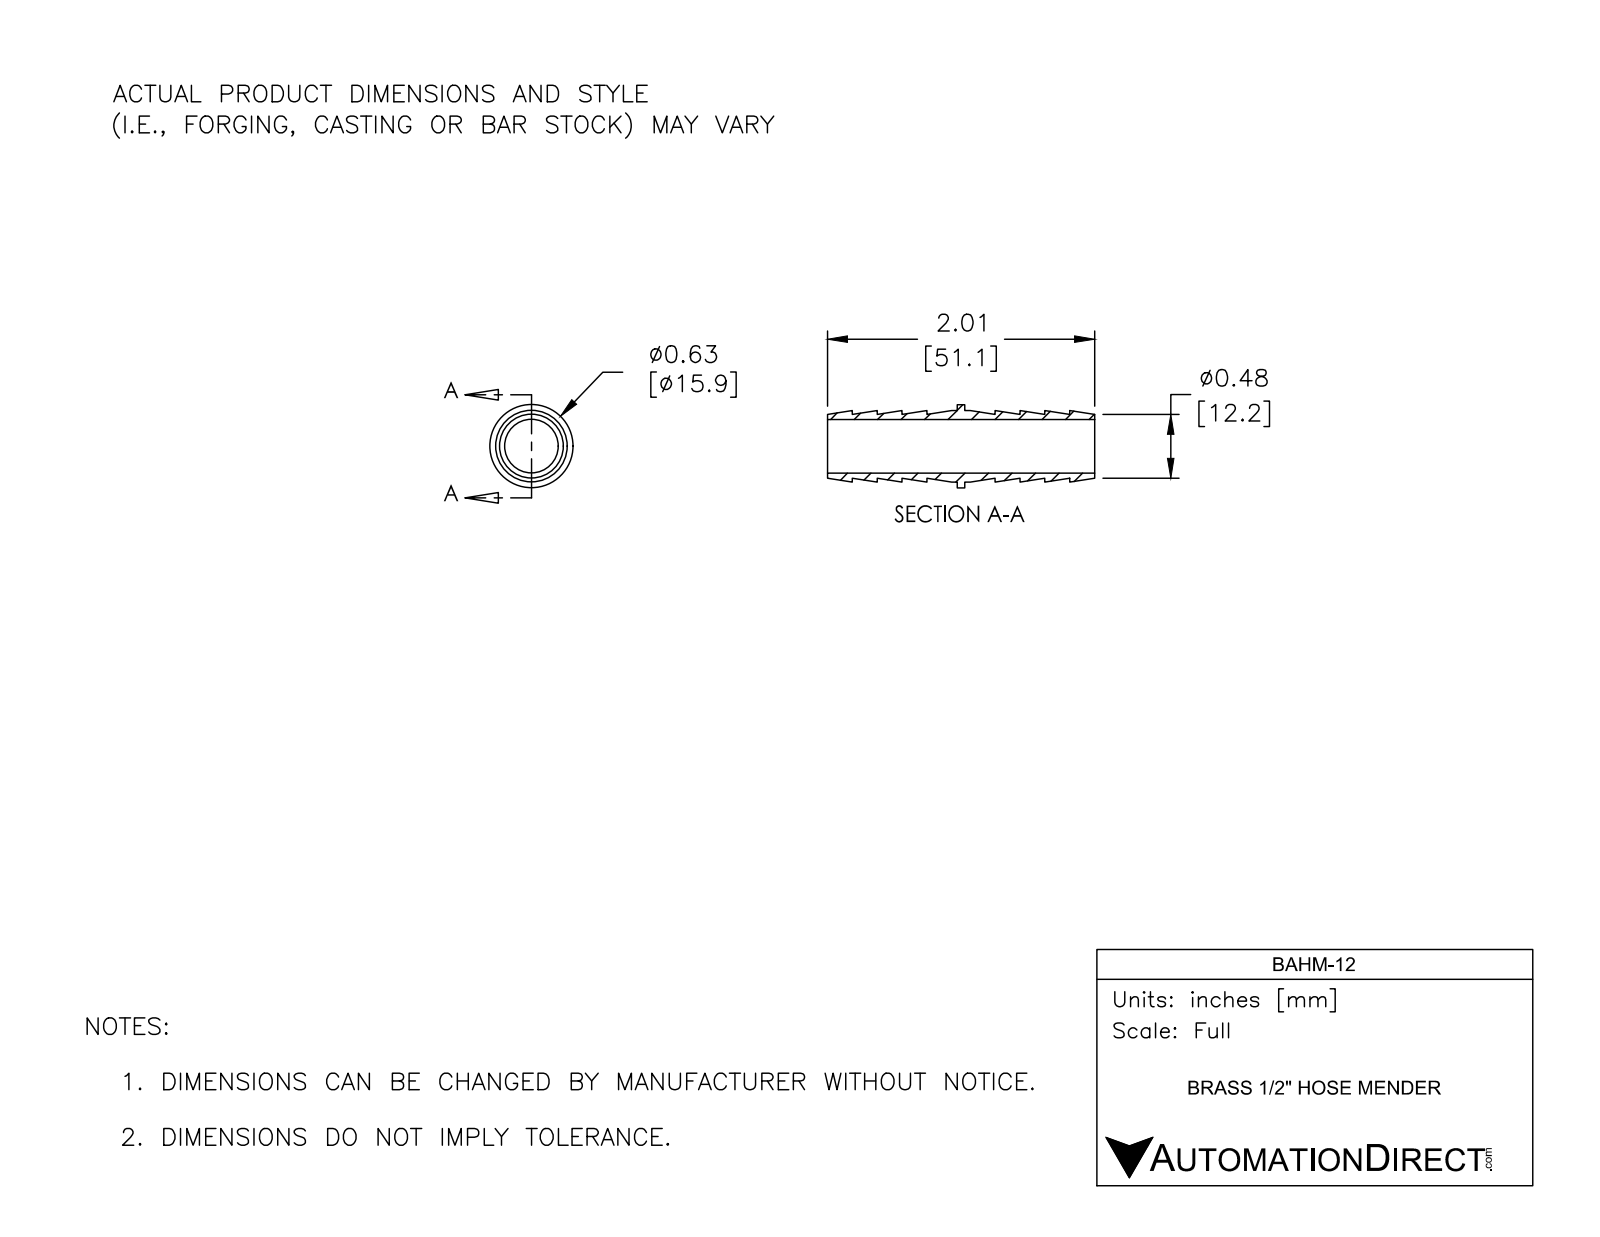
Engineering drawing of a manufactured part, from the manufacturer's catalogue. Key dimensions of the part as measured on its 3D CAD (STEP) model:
Part name (STEP PRODUCT): BAHM-12
STEP written by: SolidWorks 2017 (AUTOMOTIVE_DESIGN)
Units: inches
Bodies: 1 solid, 40 faces (12 planar, 8 cylindrical, 20 other)
Overall size (bounding box): 2.01 × 0.625 × 0.625
Volume: 0.162 in³ · Surface area: 6.479 in²
Round holes (diameter × count): ⌀0.403 ×1
Round bosses / shafts (diameter × count): ⌀0.625 ×1, ⌀0.54 ×1
Main face-to-face distances: 0.187, 0.374, 1.262, 0.561, 1.449, 1.075, 1.636, 0.888, 0.977, 1.033
